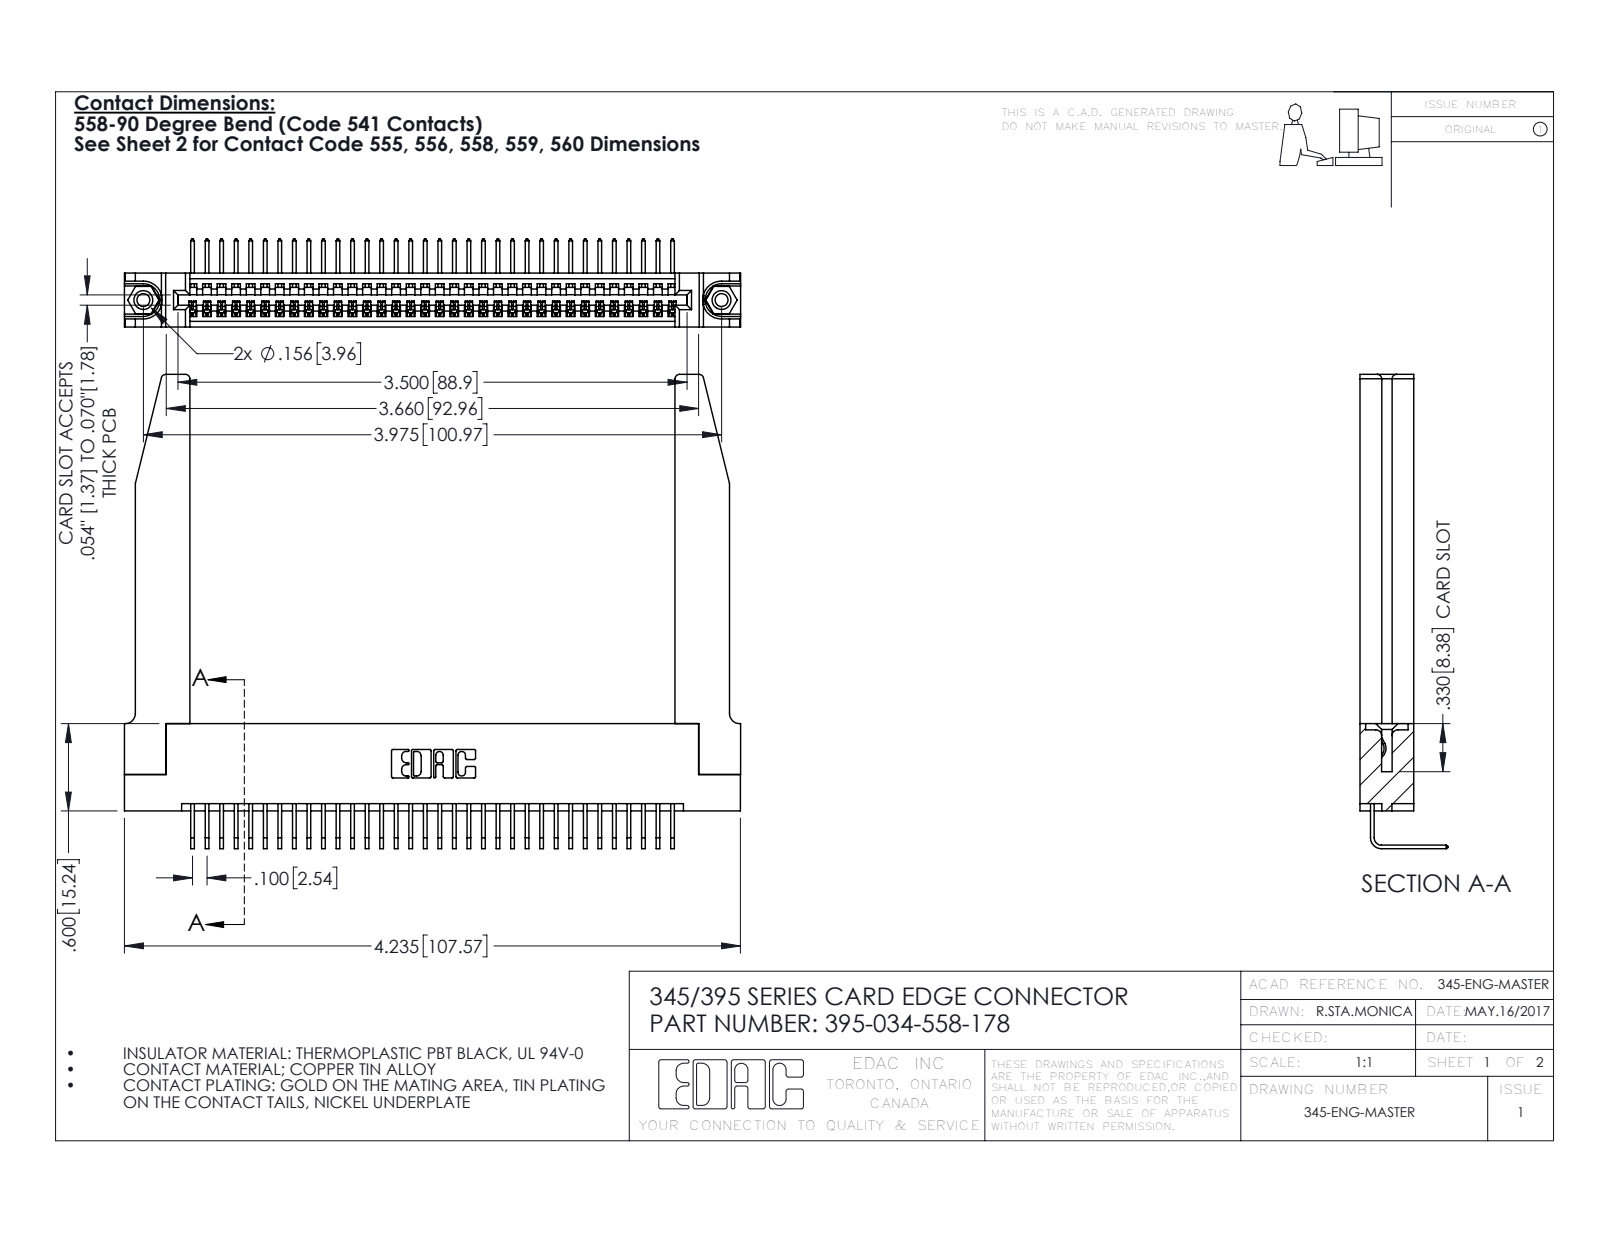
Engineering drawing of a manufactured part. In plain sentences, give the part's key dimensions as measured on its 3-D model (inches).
The part is named "345 Part_Flush Mounting Lugs - 0.156 Dia-TH; 345-292-001_558 Tail - 2; 345-250-001_345-250-001-102; 395-034-558-178 (+1 more)". Its 3-D file was written by "SolidWorks 2016 (CONFIG_CONTROL_DESIGN)". It is 39 solids with 2400 faces: 1650 planar, 698 cylindrical and 52 other. Overall it measures 4.236 by 3.259 by 0.605 inches. Its volume is 1.101 cubic inches and its surface area 32.62 square inches. Round holes: 2 of diameter 0.089, 2 of diameter 0.125, 2 of diameter 0.156, 1 of diameter 0.064. Round bosses or shafts: 2 of diameter 0.155. Partial cylindrical surfaces (rounded edges, fillets, slot ends): 68 of radius 0.006, 22 of radius 0.01, 8 of radius 0.03, 6 of radius 0.007, 6 of radius 0.031, 3 of radius 0.026, 2 of radius 0.031, 2 of radius 0.04. The main face-to-face distances are 0.37, 0.072, 0.298, 0.2, 0.098, 0.272, 0.025, 0.225, 0.15, 0.148. The hole center spacings are 0.27, 3.74, 3.975.
